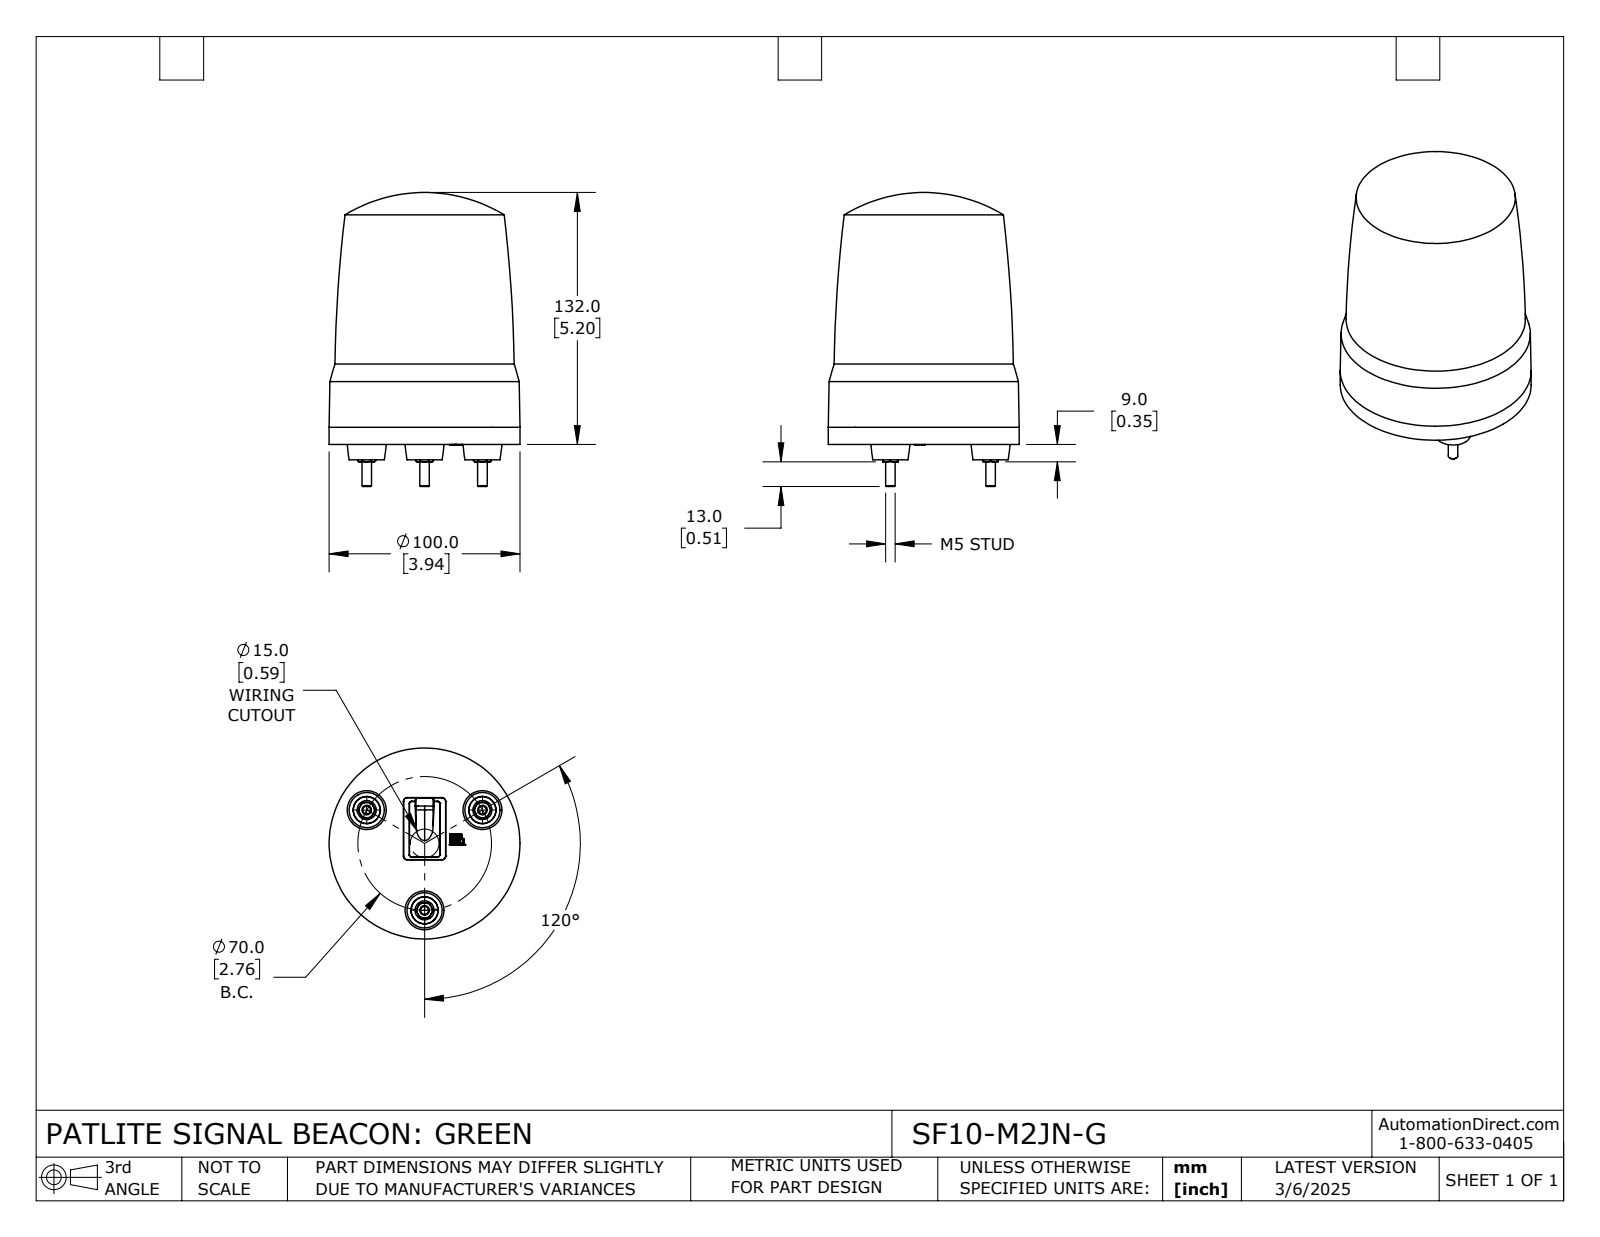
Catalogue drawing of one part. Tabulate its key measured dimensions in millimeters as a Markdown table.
| quantity | value |
| --- | --- |
| part name | SF10-M2JN-G |
| STEP written by | SolidWorks 2024 (CONFIG_CONTROL_DESIGN) |
| units | millimeters |
| bodies | 1 solid, 327 faces (159 planar, 14 cylindrical, 154 other) |
| overall size | 154 × 100 × 100 |
| volume | 859 960 mm³ |
| surface area | 52 586 mm² |
| round bosses / shafts (diameter × count) | 10 × 3, 5 × 3, 100 × 1 |
| main face-to-face distances | 8, 0.85, 8.85, 1.6, 10.45, 2.45, 3.8, 4.2, 5.05, 6.65 |
